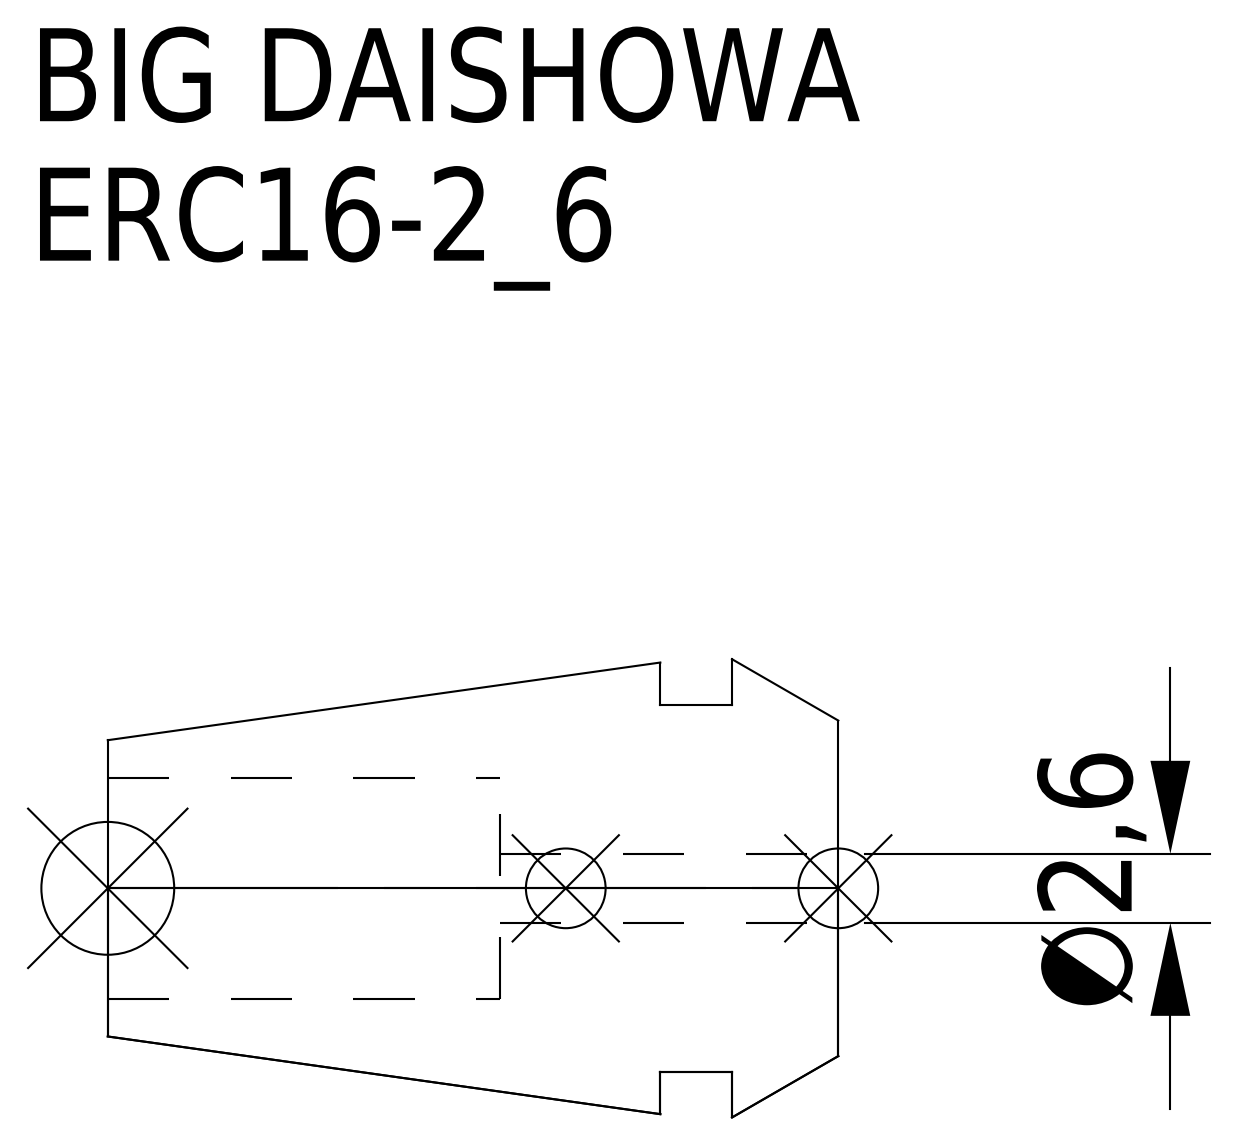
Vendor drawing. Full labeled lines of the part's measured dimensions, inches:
Part name (STEP PRODUCT): ERC16-2_6
STEP written by: CREO PARAMETRIC BY PTC INC, 2016380 (AUTOMOTIVE_DESIGN)
Units: inches
Bodies: 1 solid, 15 faces (5 planar, 6 cylindrical, 4 other)
Overall size (bounding box): 1.083 × 0.679 × 0.679
Volume: 0.215 in³ · Surface area: 3.295 in²
Round holes (diameter × count): ⌀0.102 ×1, ⌀0.327 ×1
Round bosses / shafts (diameter × count): ⌀0.543 ×1
Main face-to-face distances: 0.157, 0.264, 0.106, 0.501, 0.344, 0.237, 1.083, 0.925, 0.819, 0.581
